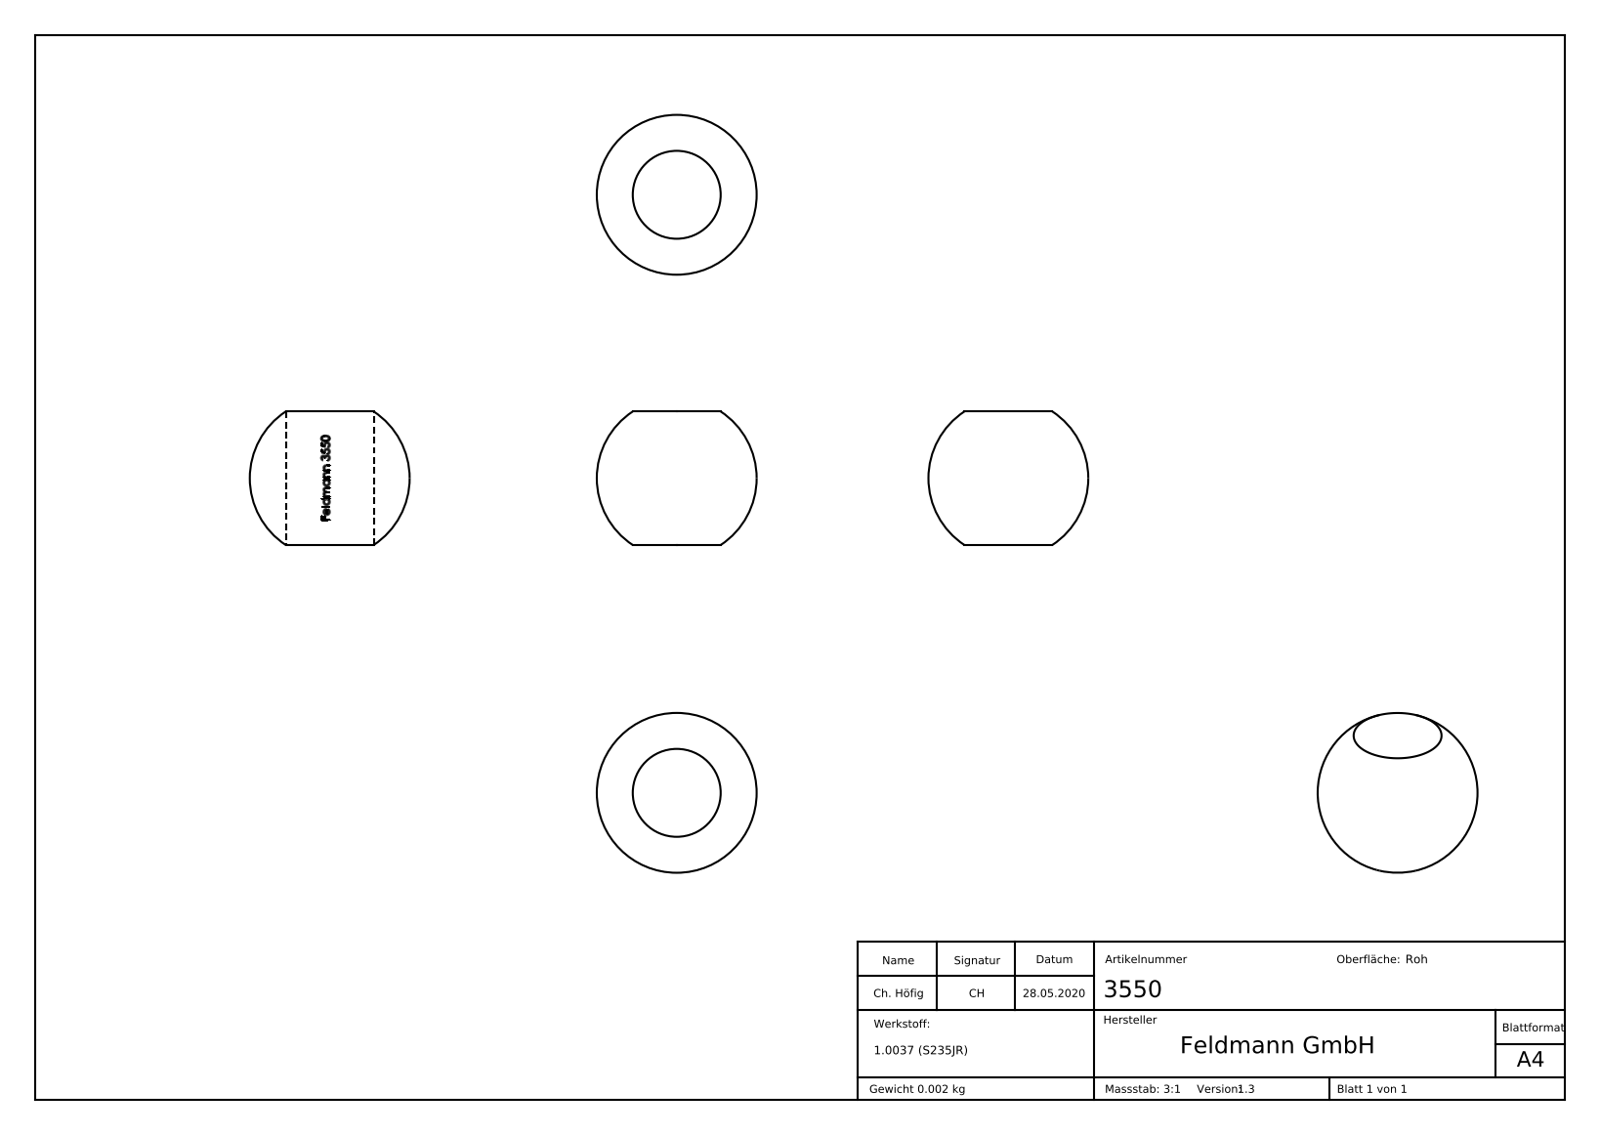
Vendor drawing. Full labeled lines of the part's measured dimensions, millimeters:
Part name (STEP PRODUCT): 3550
STEP written by: SolidWorks 2015 (CONFIG_CONTROL_DESIGN)
Units: millimetres
Bodies: 1 solid, 174 faces (69 planar, 17 cylindrical, 88 other)
Overall size (bounding box): 10 × 10 × 8.35
Volume: 305 mm³ · Surface area: 410 mm²
Round holes (diameter × count): ⌀5.5 ×1
Partial cylindrical surfaces — rounded edges, fillets, slot ends (radius × count): R2.85 ×1
Main face-to-face distances: 0.45, 0.55, 0.4, 0.5, 0.81, 0.53, 1.79, 1.84, 1.19, 1.74
